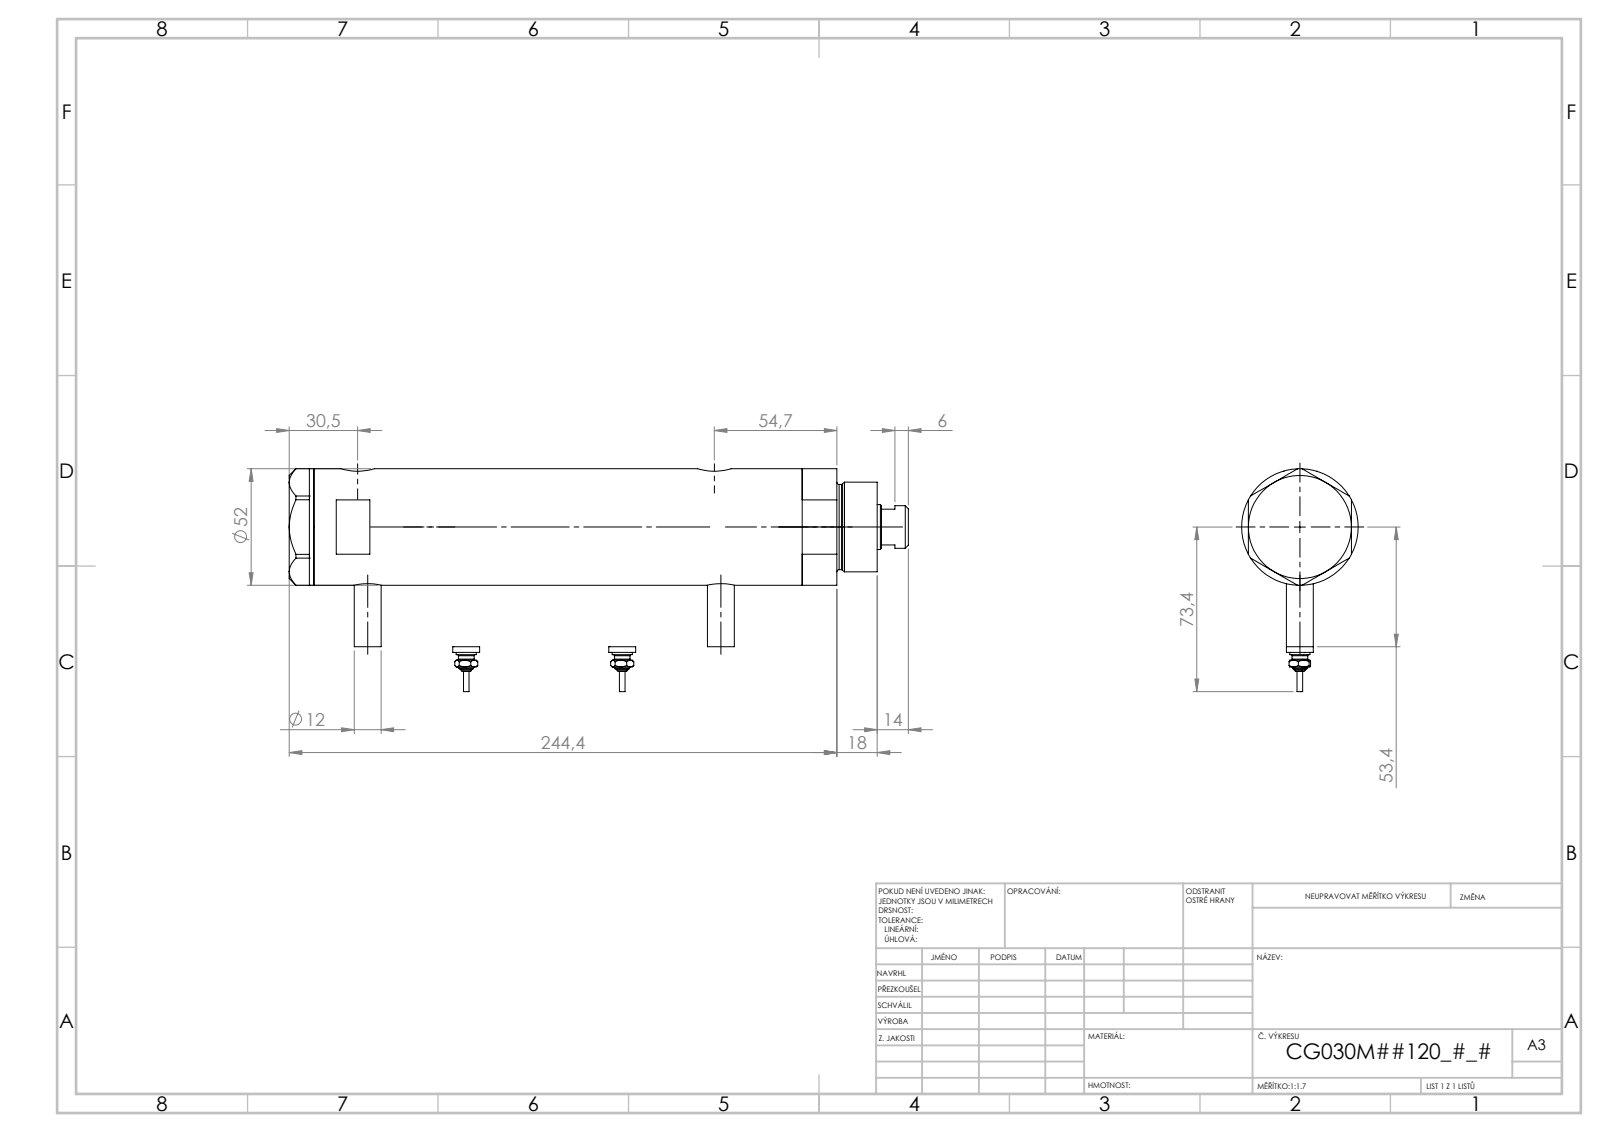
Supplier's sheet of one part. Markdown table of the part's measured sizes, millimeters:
| quantity | value |
| --- | --- |
| part name | V270CG_BACK; V270CG_VC; V270CG_SWITCH; V270CG_FRONT (+1 more) |
| STEP written by | SolidWorks 2019 (CONFIG_CONTROL_DESIGN) |
| units | millimeters |
| bodies | 6 solids, 246 faces (95 planar, 77 cylindrical, 74 other) |
| overall size | 269.02 × 84.3 × 52 |
| volume | 478 097 mm³ |
| surface area | 105 489 mm² |
| round holes (diameter × count) | 5 × 2, 9.73 × 2, 12.5 × 2, 15 × 2, 6.5 × 1, 20 × 1, 21.5 × 1, 30 × 1, 33 × 1, 44 × 1 |
| round bosses / shafts (diameter × count) | 12 × 3, 9 × 2, 7 × 2, 4.34 × 2, 2.4 × 2, 52 × 1, 40 × 1, 38 × 1 |
| main face-to-face distances | 23.8, 11, 34.8, 46, 184.54, 173.54, 149.74, 220.94, 209.94, 186.14 |
| hole center spacings | 2.9, 4.5, 146.75, 149.65, 151.25, 154.15, 2.89, 2.91 |
